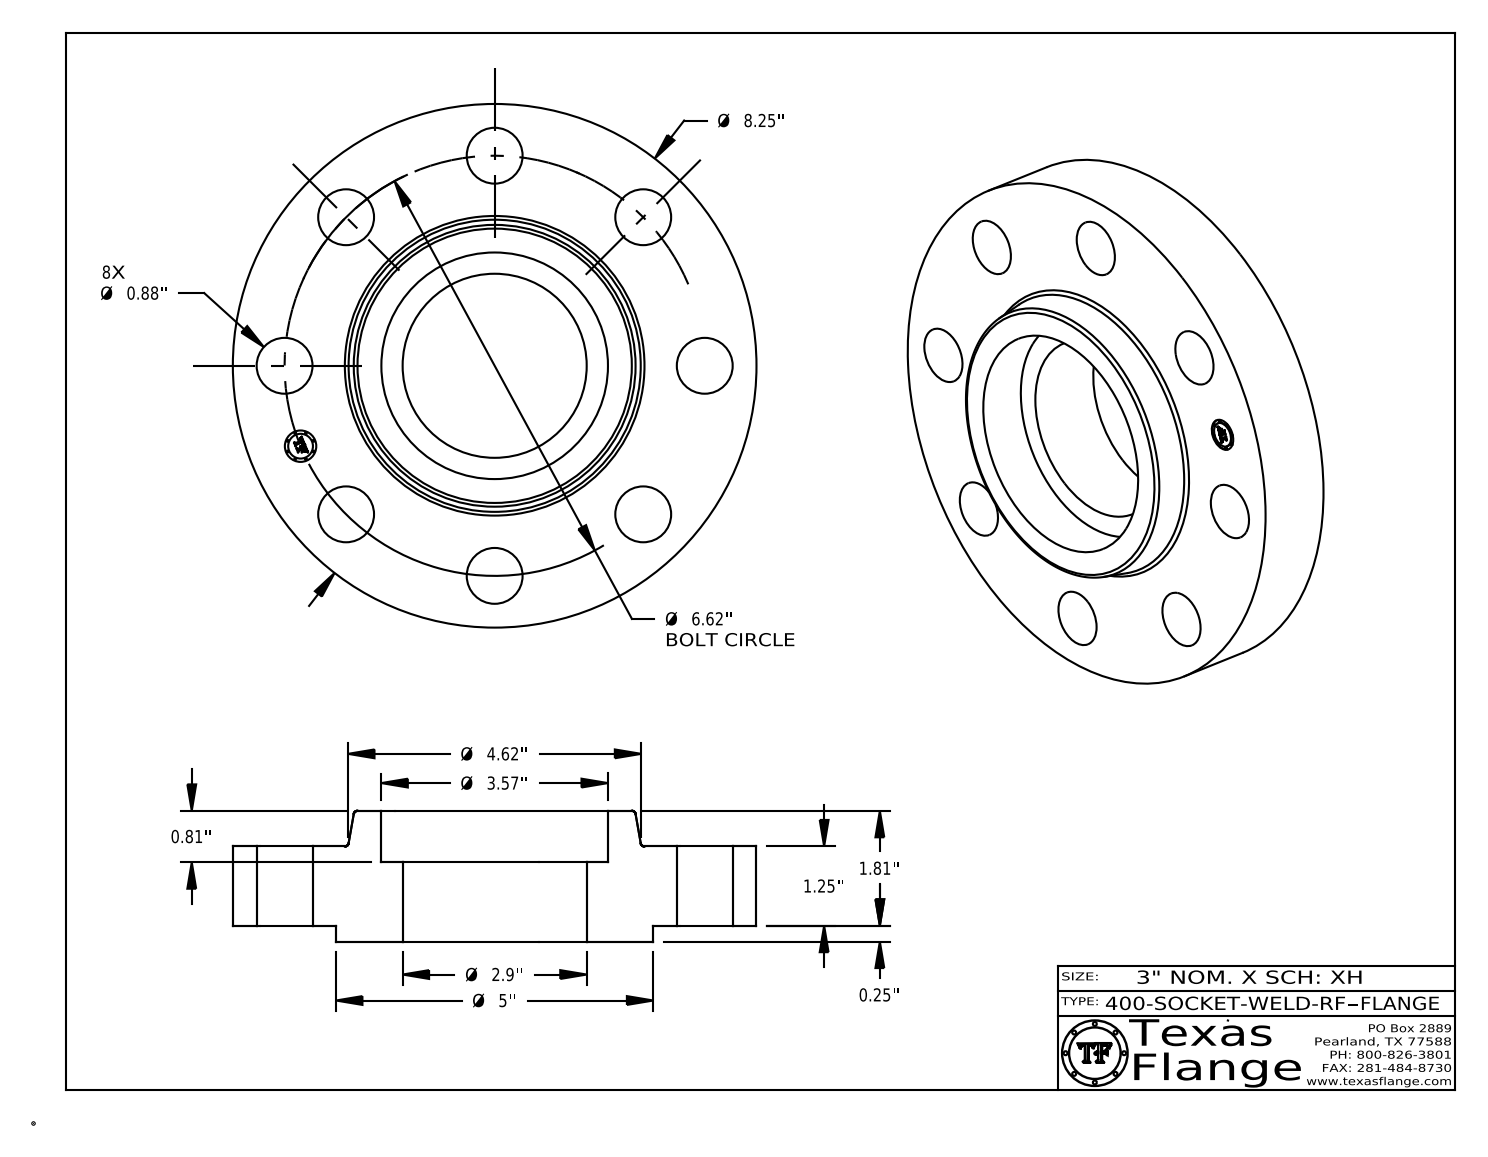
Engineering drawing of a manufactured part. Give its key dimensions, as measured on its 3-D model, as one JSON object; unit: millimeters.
{"part_name": "400-SOCKET-WELD-RF", "step_written_by": "CATIA V5 STEP AP214 (AUTOMOTIVE_DESIGN)", "units": "millimeters", "bodies": {"solids": 1, "faces": 420, "planar": 370, "cylindrical": 44, "other": 6}, "overall_size": [209.6, 209.6, 52.3], "volume_mm3": 954900, "surface_area_mm2": 112700, "round_holes": [[22.4, 8], [12.6, 1], [73.7, 1], [90.7, 1]], "round_bosses_or_shafts": [[0.8, 8], [209.6, 1], [127, 1], [9.9, 1]], "face_to_face_distances": [31.8, 6.4, 38.1, 52.3, 46, 14.2, 25.4, 20.6, 0.4, 37.7], "hole_center_spacings": [84.1, 64.3, 155.3, 118.9, 118.9, 32.8, 93.4, 164.9]}
